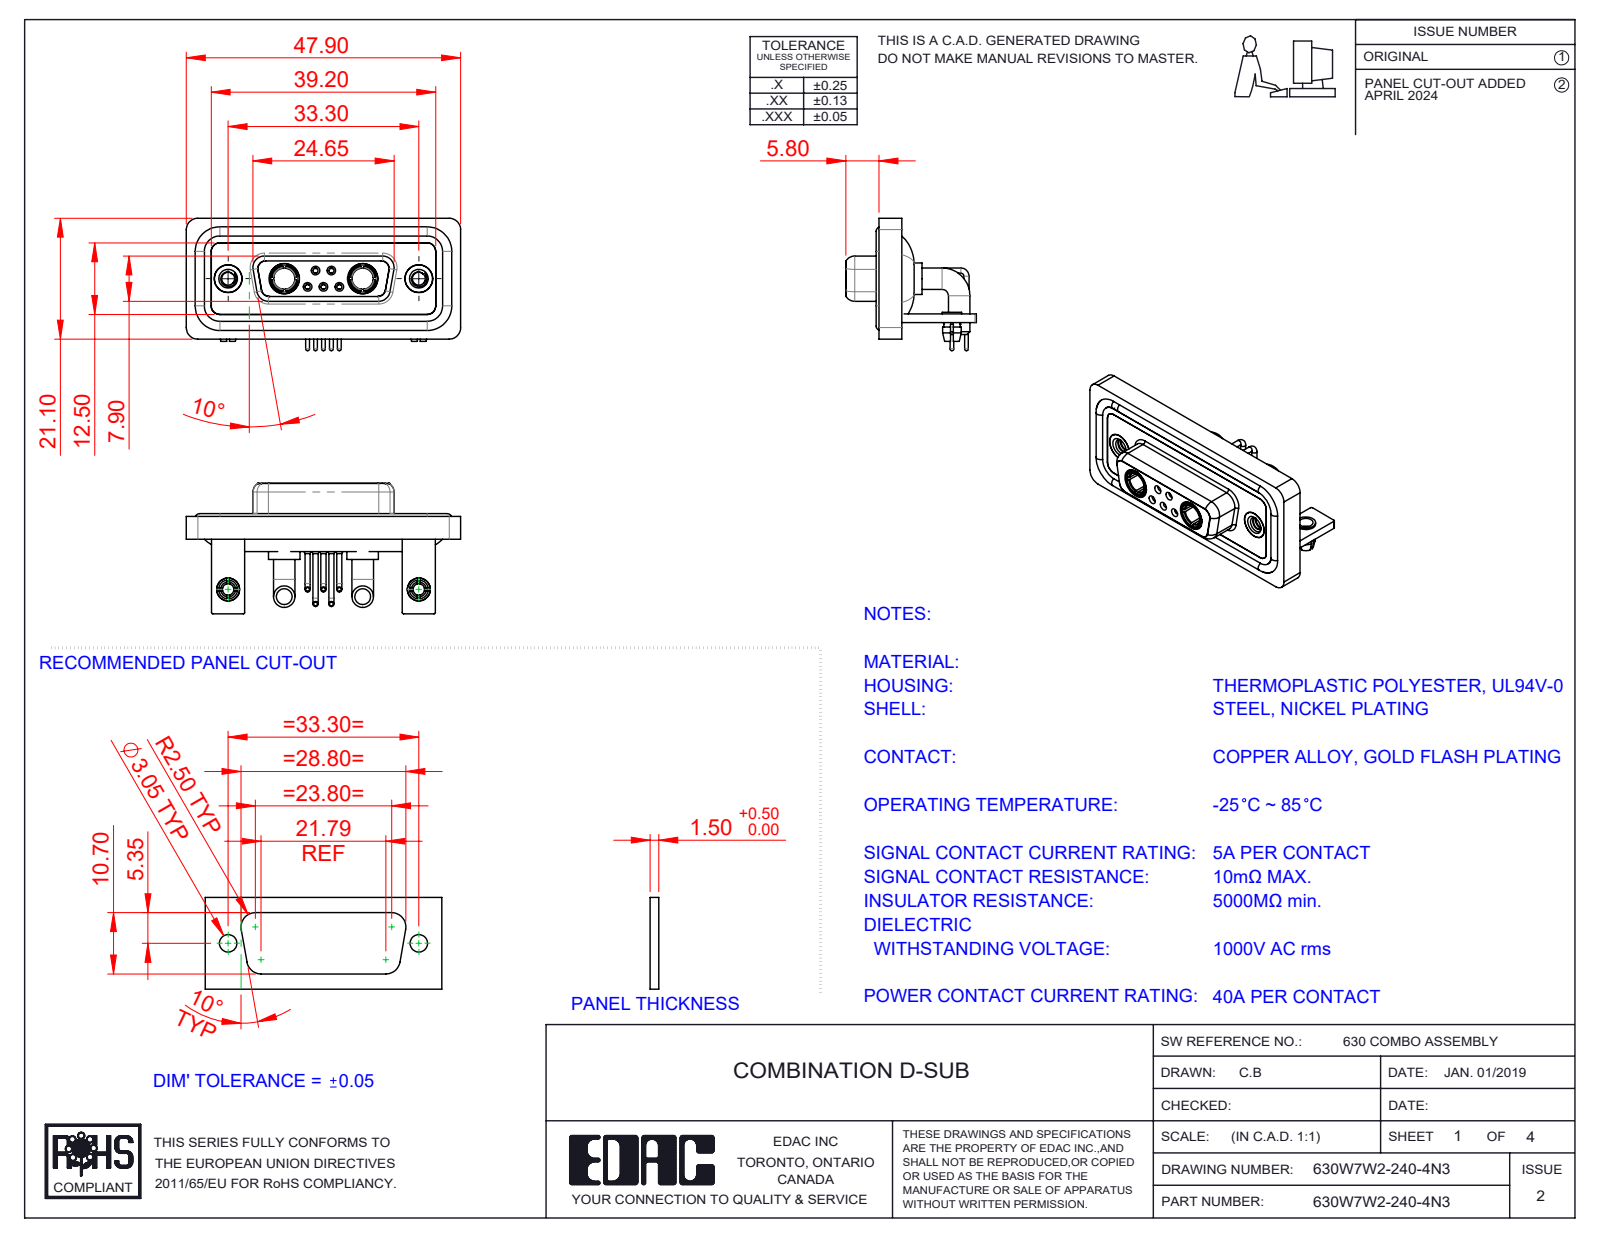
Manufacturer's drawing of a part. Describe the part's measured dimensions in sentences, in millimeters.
The part is named "630W7W2-240-4N3; 630Combo Board Lock_50 Contacts; 630Combo Waterproof Housing_15 Contacts; 630Combo Contact Row 2_50 Contacts (+7 more)". Its 3-D file was written by "SolidWorks 2023 (CONFIG_CONTROL_DESIGN)". It is 20 solids with 947 faces: 306 planar, 409 cylindrical and 232 other. Overall it measures 47.9 by 23.12 by 22.8 millimeters. Its volume is 6 744 cubic millimeters and its surface area 11 239 square millimeters. Round holes: 7 of diameter 2, 5 of diameter 0.9, 5 of diameter 1.1, 5 of diameter 1.5, 4 of diameter 4.85, 3 of diameter 1.6, 2 of diameter 1.7, 2 of diameter 2.26, 2 of diameter 2.5, 2 of diameter 3.2, 2 of diameter 3.7, 2 of diameter 4. Round bosses or shafts: 6 of diameter 1.6, 5 of diameter 0.9, 5 of diameter 0.65, 4 of diameter 3.75, 2 of diameter 5.5, 2 of diameter 5.2, 2 of diameter 4.96, 2 of diameter 4.95. Partial cylindrical surfaces (rounded edges, fillets, slot ends): 21 of radius 2, 18 of radius 1.5, 16 of radius 0.25, 12 of radius 1.35, 8 of radius 1.6, 5 of radius 0.5, 4 of radius 0.6, 4 of radius 0.65. The main face-to-face distances are 0.4, 2.9, 1.5, 1.8, 3.7, 1.1, 4.1, 1.6, 2.5, 1.4. The hole center spacings are 3.16, 2.77, 9.8, 23.5, 33.3, 4.31, 4.33, 5.03.
